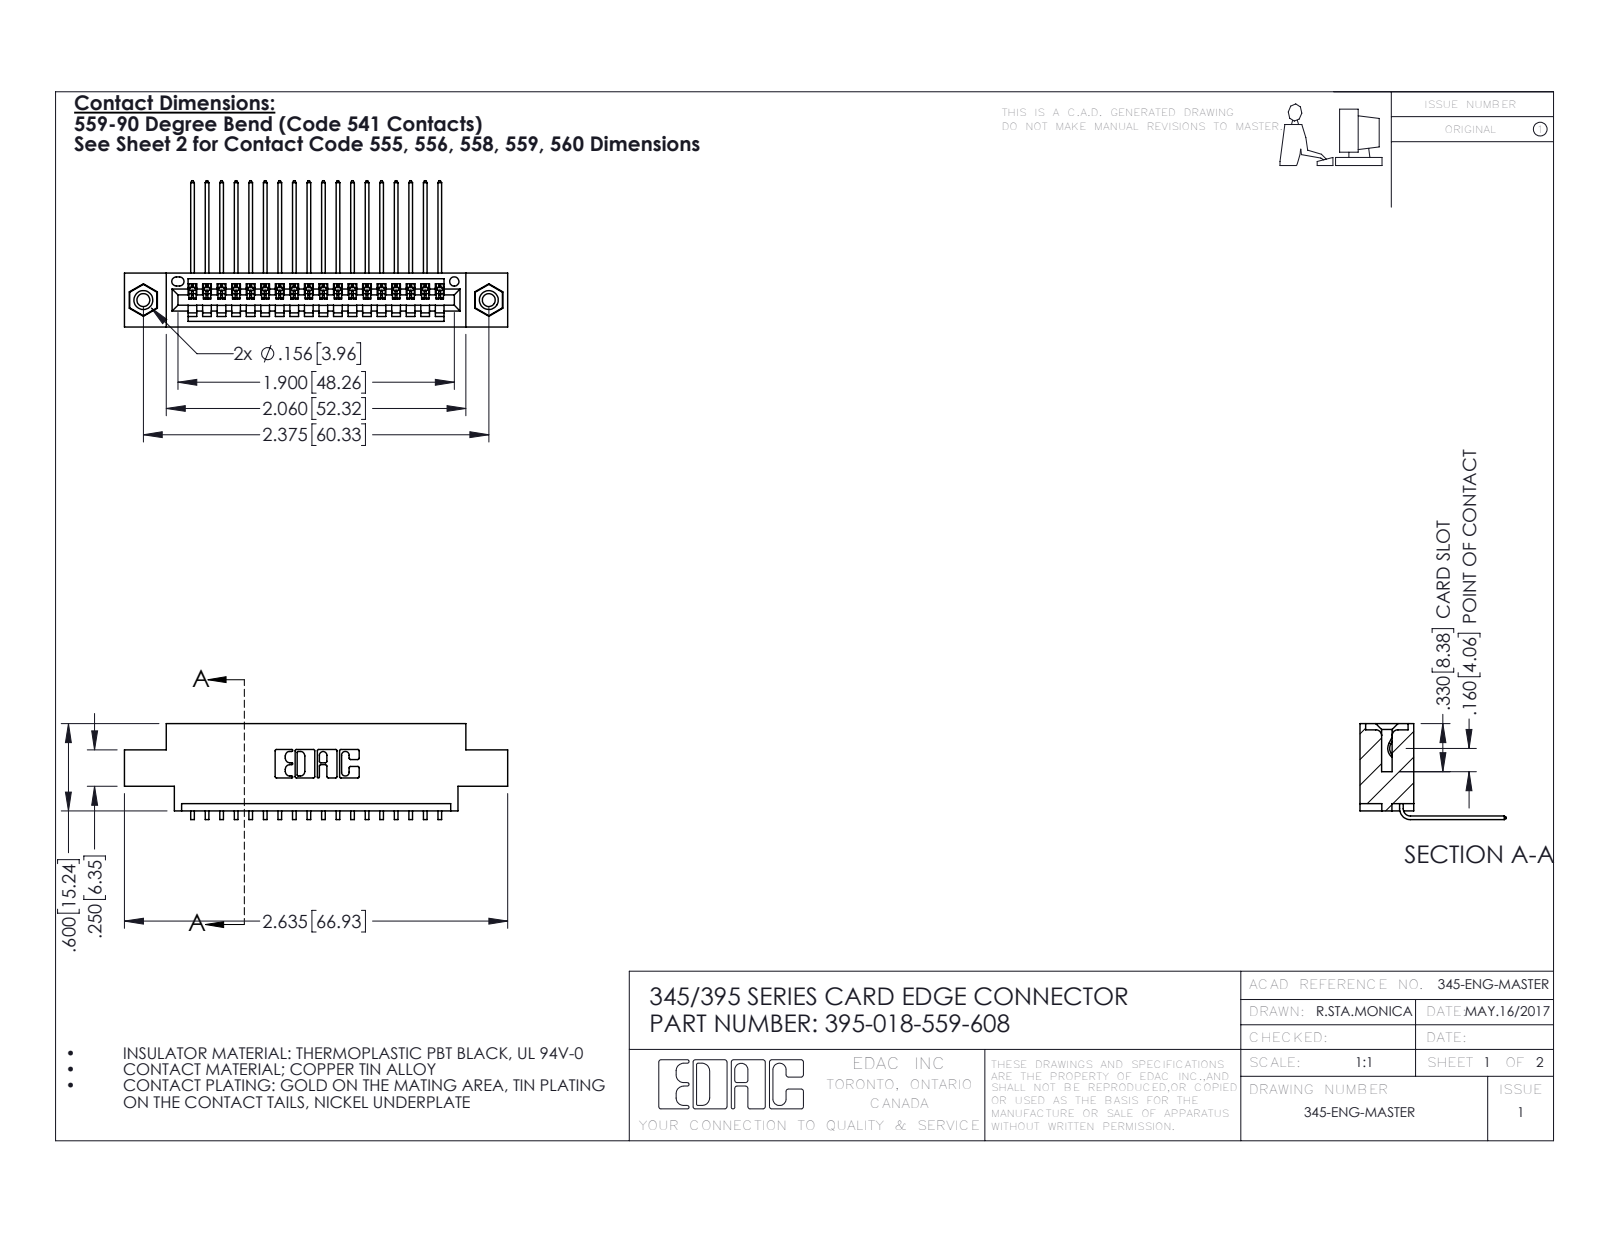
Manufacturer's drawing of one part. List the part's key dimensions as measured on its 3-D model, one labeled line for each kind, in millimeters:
Part name (STEP PRODUCT): 345-292-001_558 559 Tail - 1; 345 Part_0.170 Offset - 0.156 Dia-TI; 395-018-559-608; 345-250-001_345-250-003-102
STEP written by: SolidWorks 2016 (CONFIG_CONTROL_DESIGN)
Units: millimetres
Bodies: 21 solids, 1270 faces (872 planar, 382 cylindrical, 16 other)
Overall size (bounding box): 66.9 × 25.5 × 16.7
Volume: 6 100 mm³ · Surface area: 8 277 mm²
Round holes (diameter × count): ⌀2.3 ×2, ⌀3.2 ×2, ⌀4 ×2, ⌀1.6 ×1
Round bosses / shafts (diameter × count): ⌀3.9 ×2
Partial cylindrical surfaces — rounded edges, fillets, slot ends (radius × count): R0.2 ×36, R0.3 ×22, R0.2 ×6, R0.8 ×6, R0.7 ×3, R0.8 ×2, R1 ×2, R0.4 ×1
Main face-to-face distances: 1.8, 7.6, 9.4, 5.1, 2.5, 6.9, 0.6, 5.7, 2.5, 3.8
Hole centre spacings: 6.9, 54.4, 60.3
